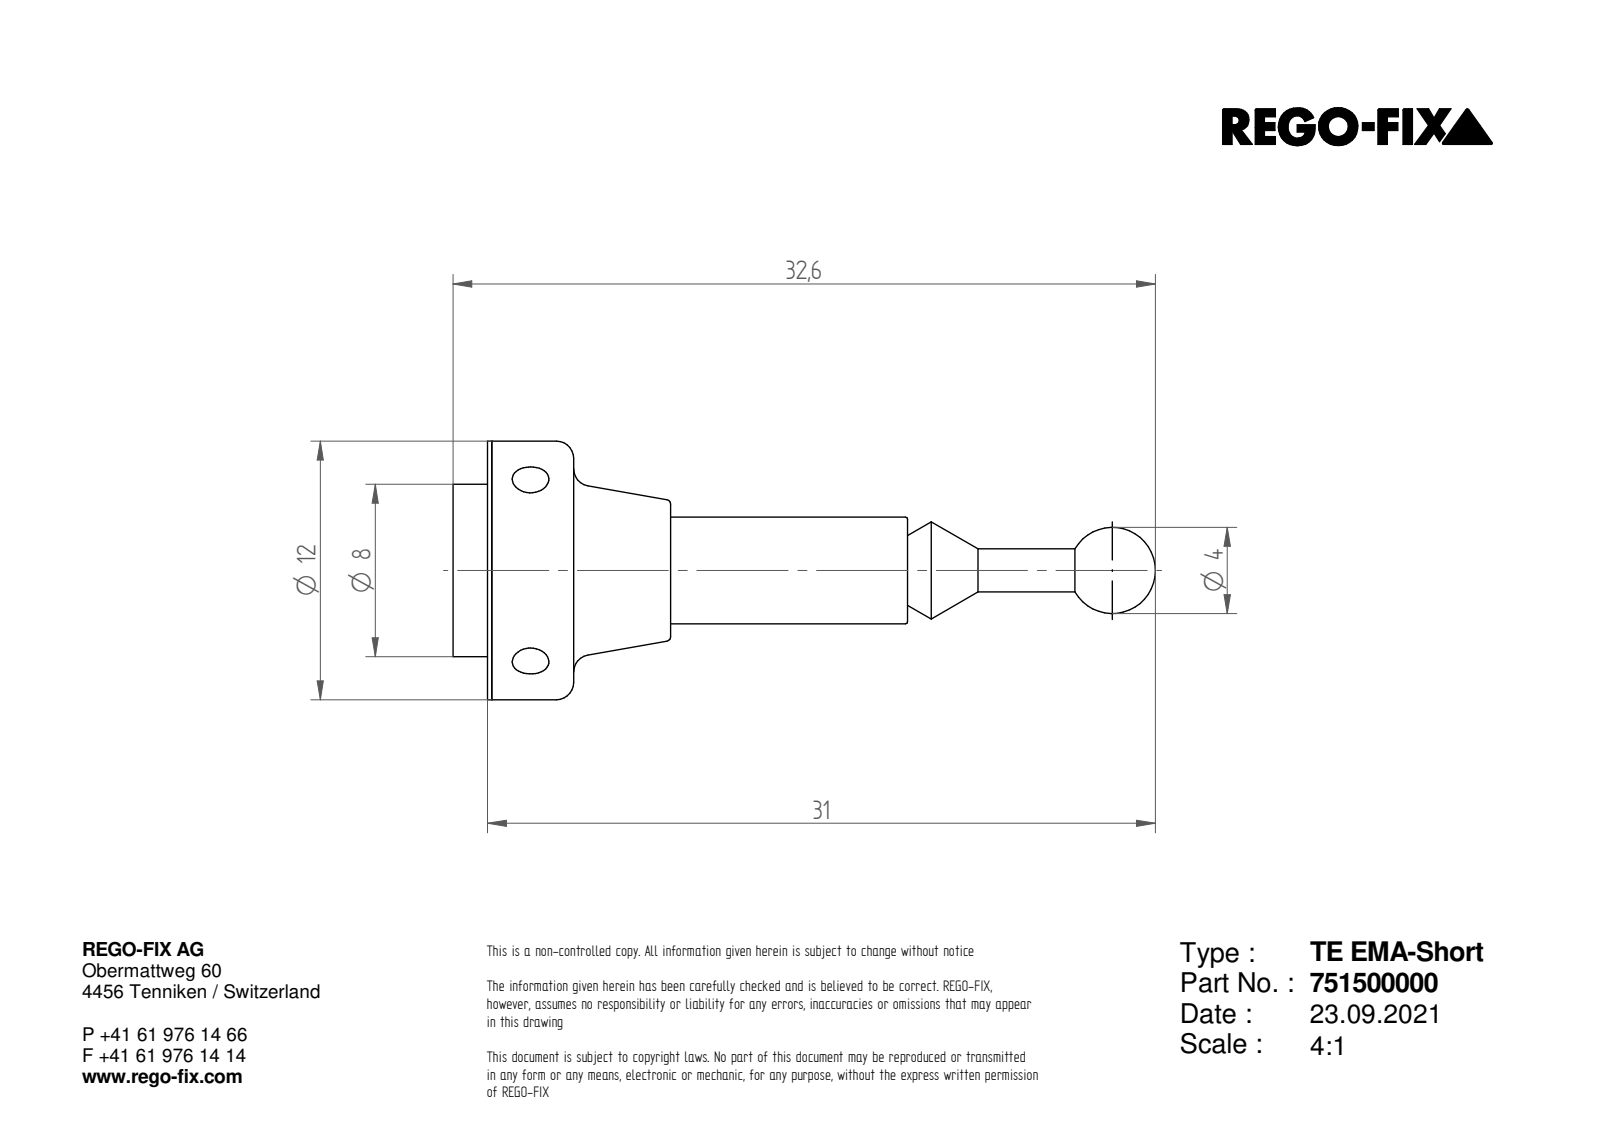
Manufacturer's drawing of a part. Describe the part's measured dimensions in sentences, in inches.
The part is named "0025251". Its 3-D file was written by "ST-DEVELOPER v16.7 (AUTOMOTIVE_DESIGN)". It is 2 solids with 28 faces: 6 planar, 9 cylindrical and 13 other. Overall it measures 1.283 by 0.472 by 0.472 inches. Its volume is 0.008 cubic inches and its surface area 1.556 square inches. Round holes: 2 of diameter 0.067. Round bosses or shafts: 1 of diameter 0.472, 1 of diameter 0.315, 1 of diameter 0.195, 1 of diameter 0.079. The main face-to-face distances are 0.071, 0.063, 0.15, 0.157, 0.22, 0.61, 0.76, 0.768, 0.831, 0.433.
